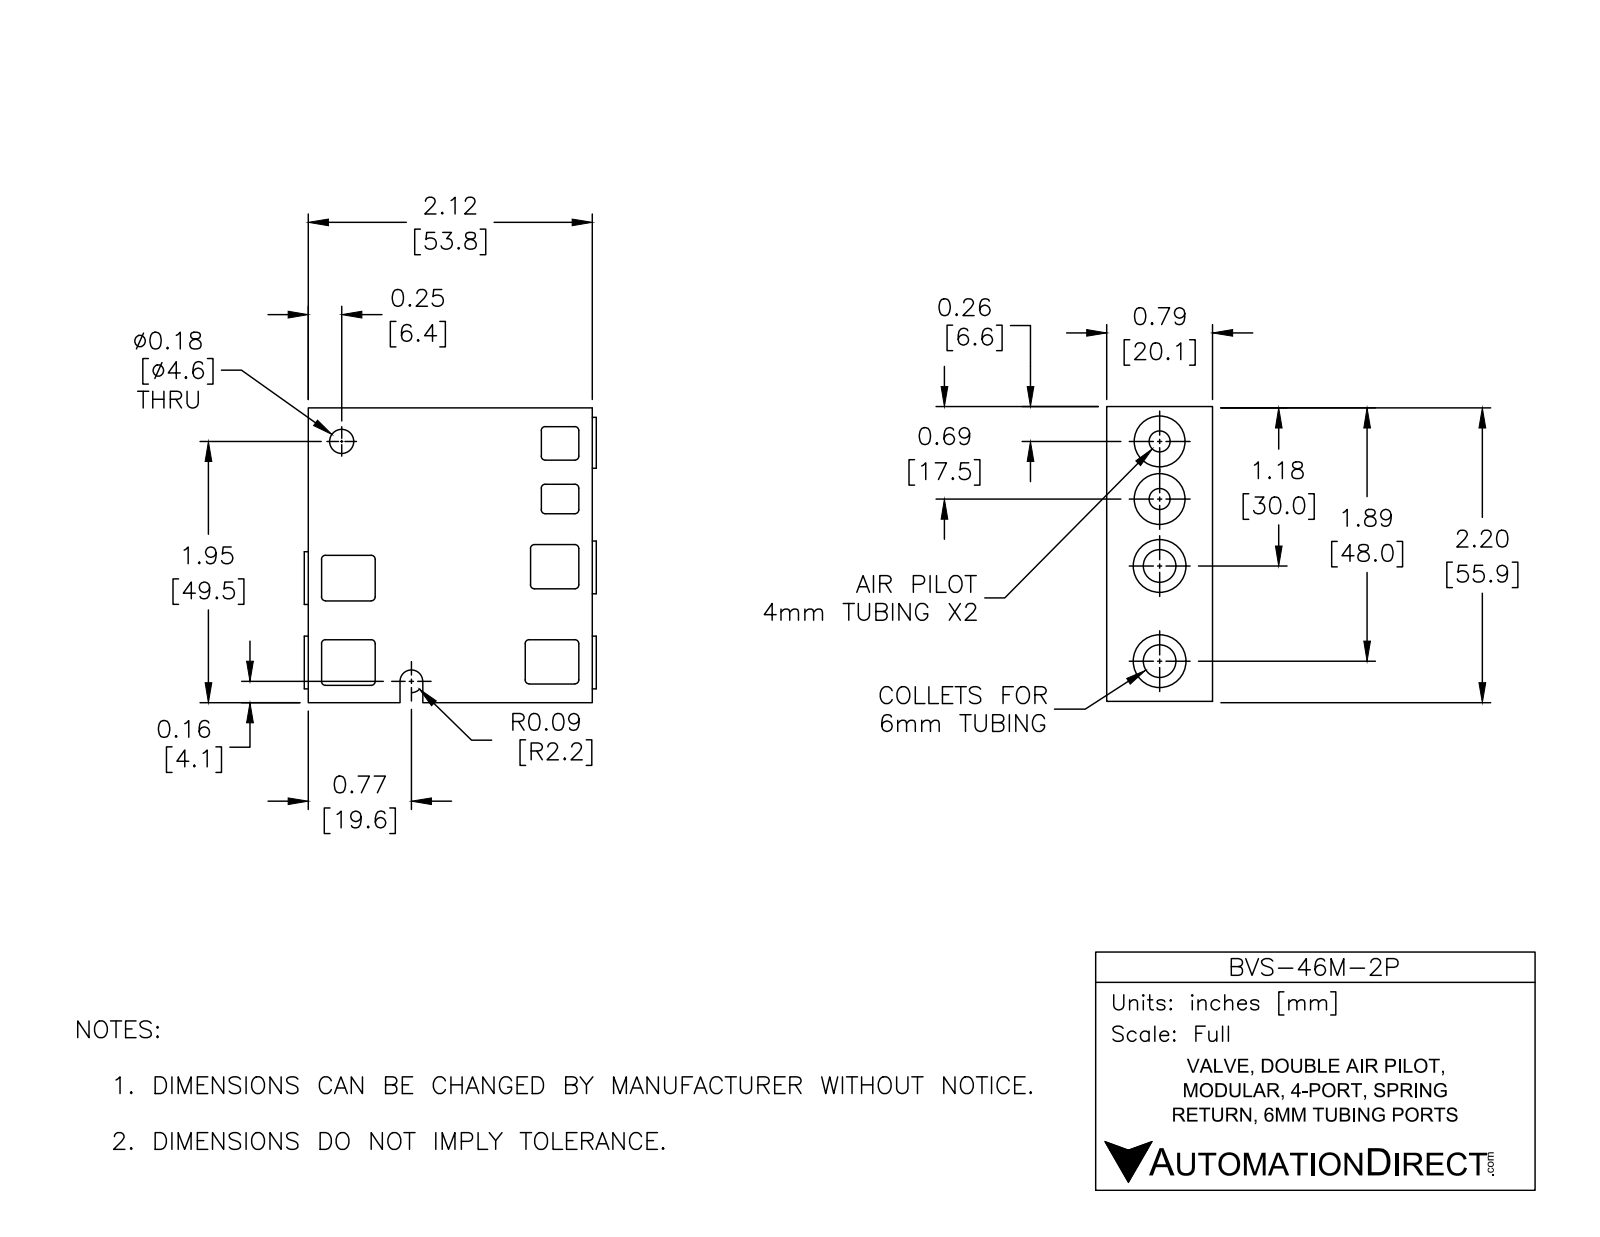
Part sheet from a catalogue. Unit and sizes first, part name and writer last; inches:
Units: inches
Overall size (bounding box): 2.2 × 2.18 × 0.79
Round holes (diameter × count): ⌀0.244 ×3, ⌀0.32 ×2, ⌀0.06 ×1, ⌀0.18 ×1
Round bosses / shafts (diameter × count): ⌀0.394 ×3, ⌀0.38 ×2
Partial cylindrical surfaces — rounded edges, fillets, slot ends (radius × count): R0.03 ×24, R0.085 ×1
Main face-to-face distances: 0.79, 0.1, 2.2, 0.69, 2.12, 0.59, 0.03, 2.15, 0.13, 0.78
Hole centre spacings: 0.08, 0.43, 0.5, 0.58, 0.63, 0.71, 0.93, 1.01
Volume: 3.262 in³ · Surface area: 22.36 in²
Bodies: 1 solid, 159 faces (82 planar, 77 cylindrical, 0 other)
Part name (STEP PRODUCT): BVS-46M-2P
STEP written by: SolidWorks 2016 (AUTOMOTIVE_DESIGN)
